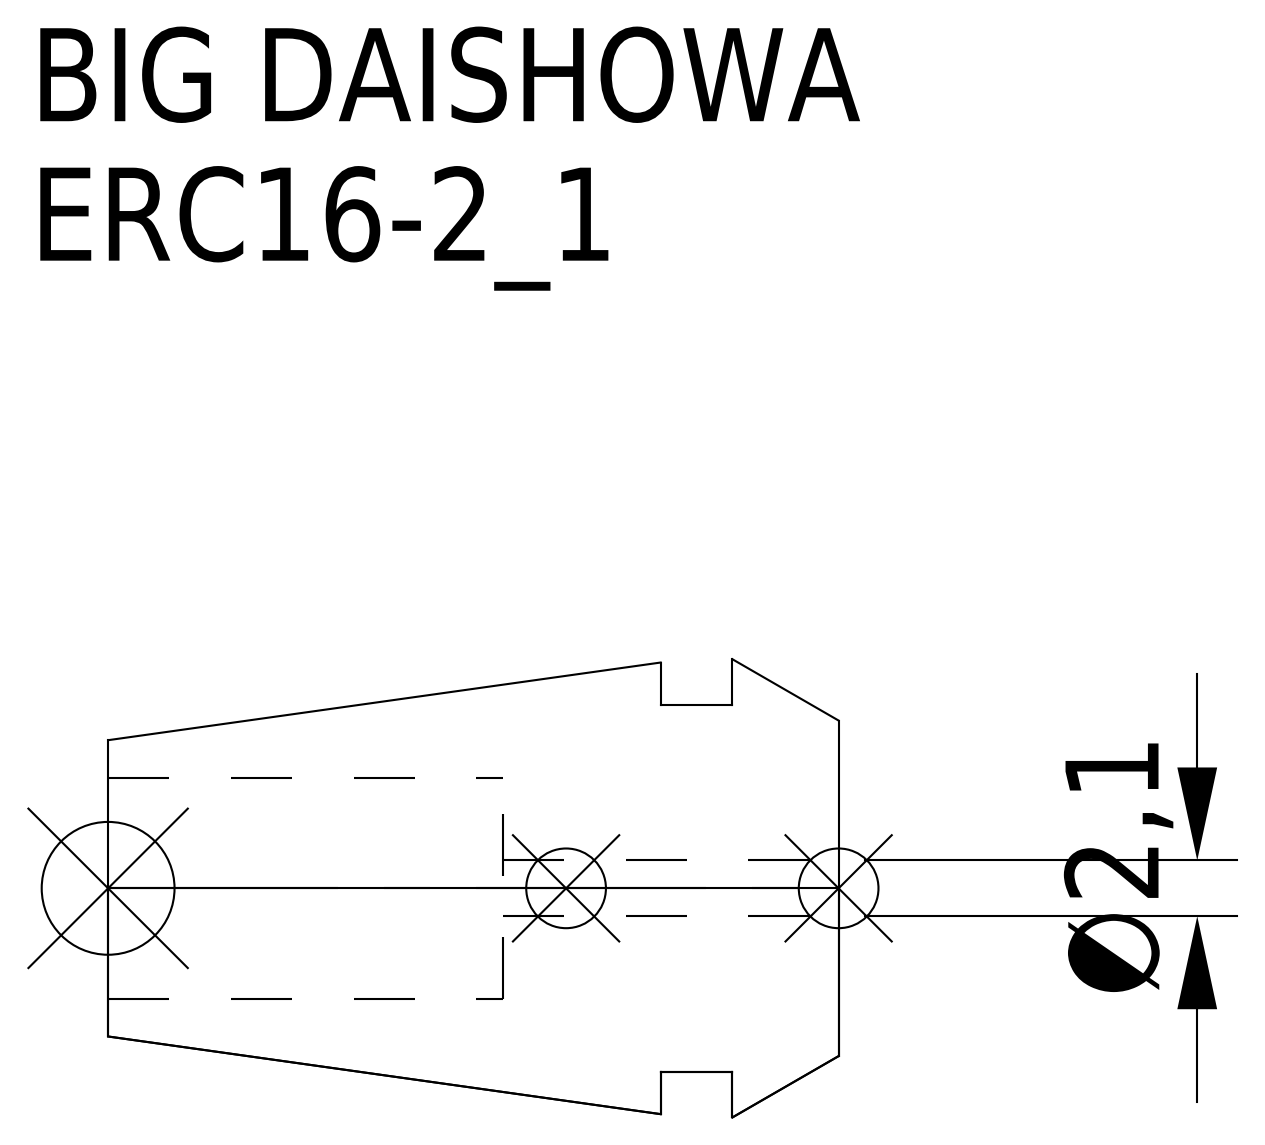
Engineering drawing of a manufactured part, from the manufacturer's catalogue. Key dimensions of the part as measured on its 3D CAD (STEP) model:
Part name (STEP PRODUCT): ERC16-2_1
STEP written by: CREO PARAMETRIC BY PTC INC, 2016380 (AUTOMOTIVE_DESIGN)
Units: millimetres
Bodies: 1 solid, 15 faces (5 planar, 6 cylindrical, 4 other)
Overall size (bounding box): 27.5 × 17.25 × 17.25
Volume: 3 547 mm³ · Surface area: 2 111 mm²
Round holes (diameter × count): ⌀2.1 ×1, ⌀8.3 ×1
Round bosses / shafts (diameter × count): ⌀13.8 ×1
Main face-to-face distances: 4, 6.7, 2.7, 12.63, 8.63, 5.93, 27.5, 23.5, 20.8, 14.87
